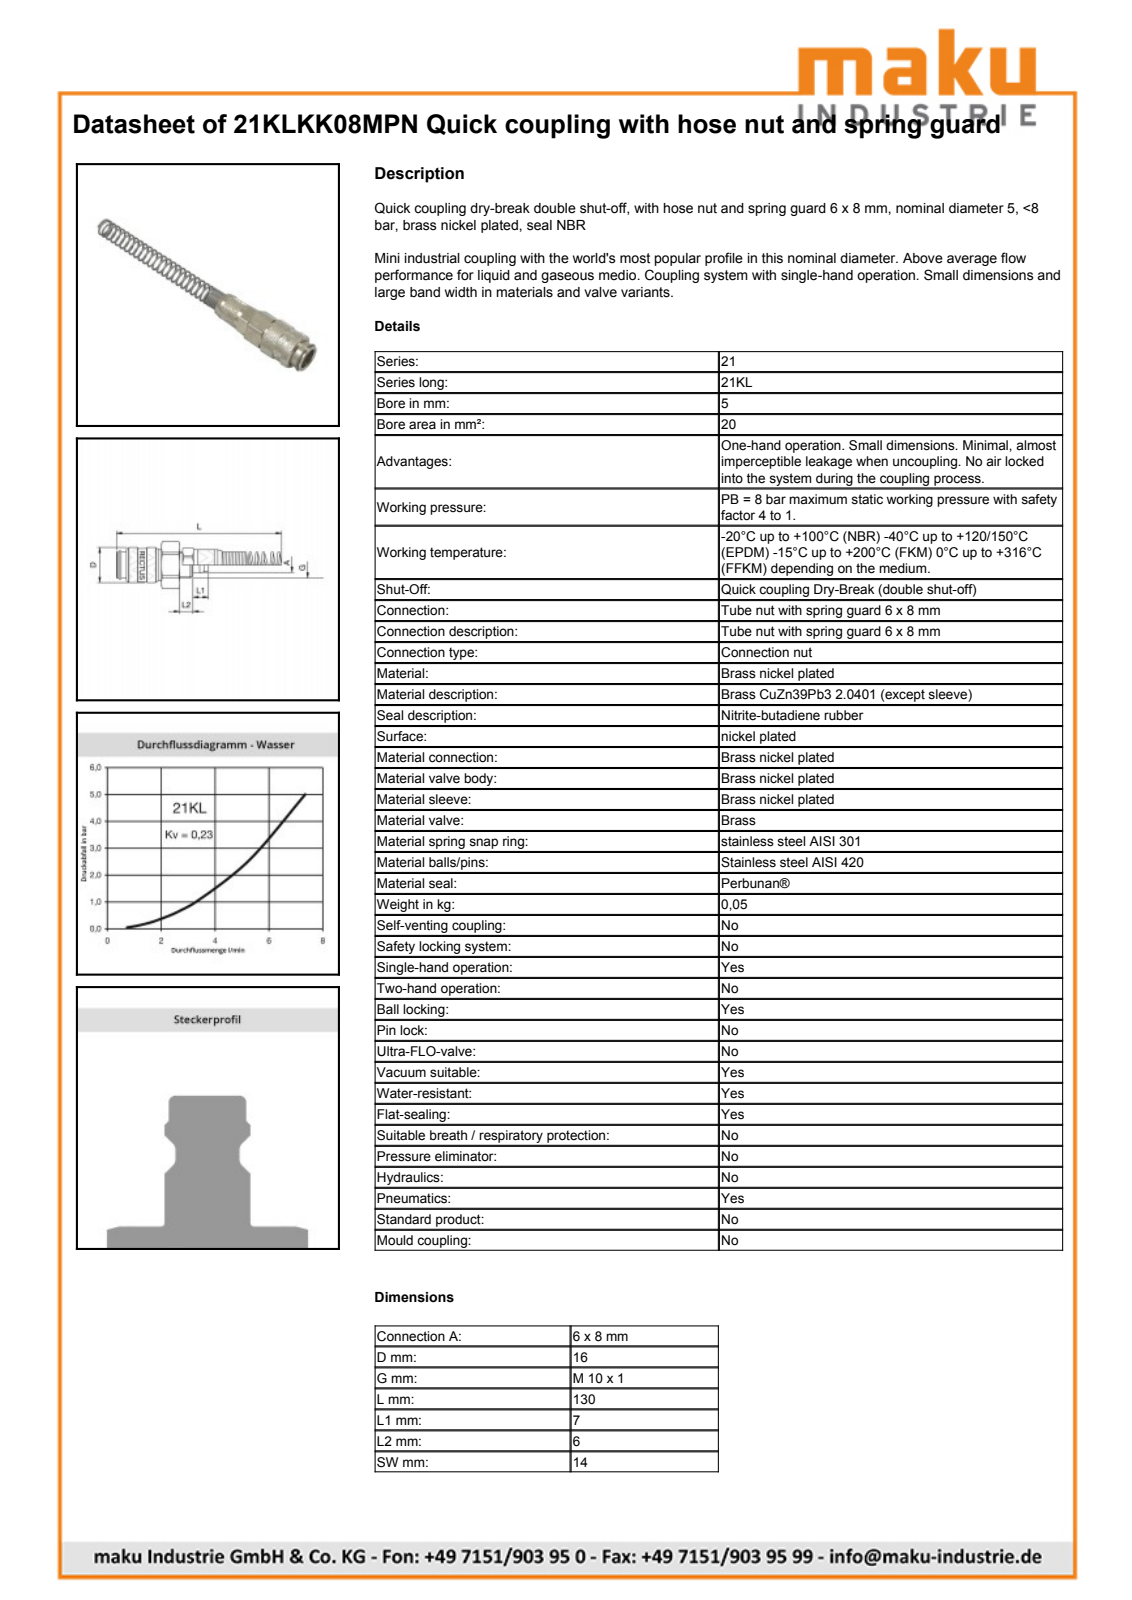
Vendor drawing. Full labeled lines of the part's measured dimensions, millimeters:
Part name (STEP PRODUCT): D113150
STEP written by: Autodesk Inventor 2013 (AUTOMOTIVE_DESIGN)
Units: millimetres
Bodies: 2 solids, 383 faces (135 planar, 57 cylindrical, 191 other)
Overall size (bounding box): 128.99 × 16 × 16
Volume: 7 421 mm³ · Surface area: 8 237 mm²
Round holes (diameter × count): ⌀12.15 ×1, ⌀12.75 ×1, ⌀14 ×1, ⌀14.6 ×1
Round bosses / shafts (diameter × count): ⌀16 ×1, ⌀15 ×1, ⌀13.5 ×1, ⌀13.4 ×1, ⌀12 ×1, ⌀11.2 ×1, ⌀6.05 ×1
Partial cylindrical surfaces — rounded edges, fillets, slot ends (radius × count): R7.4 ×1, R7.7 ×1, R7.9 ×1
Main face-to-face distances: 14, 39.45, 4.6, 34.85, 1, 14.5, 19.1, 20.35, 16.35, 11.75
